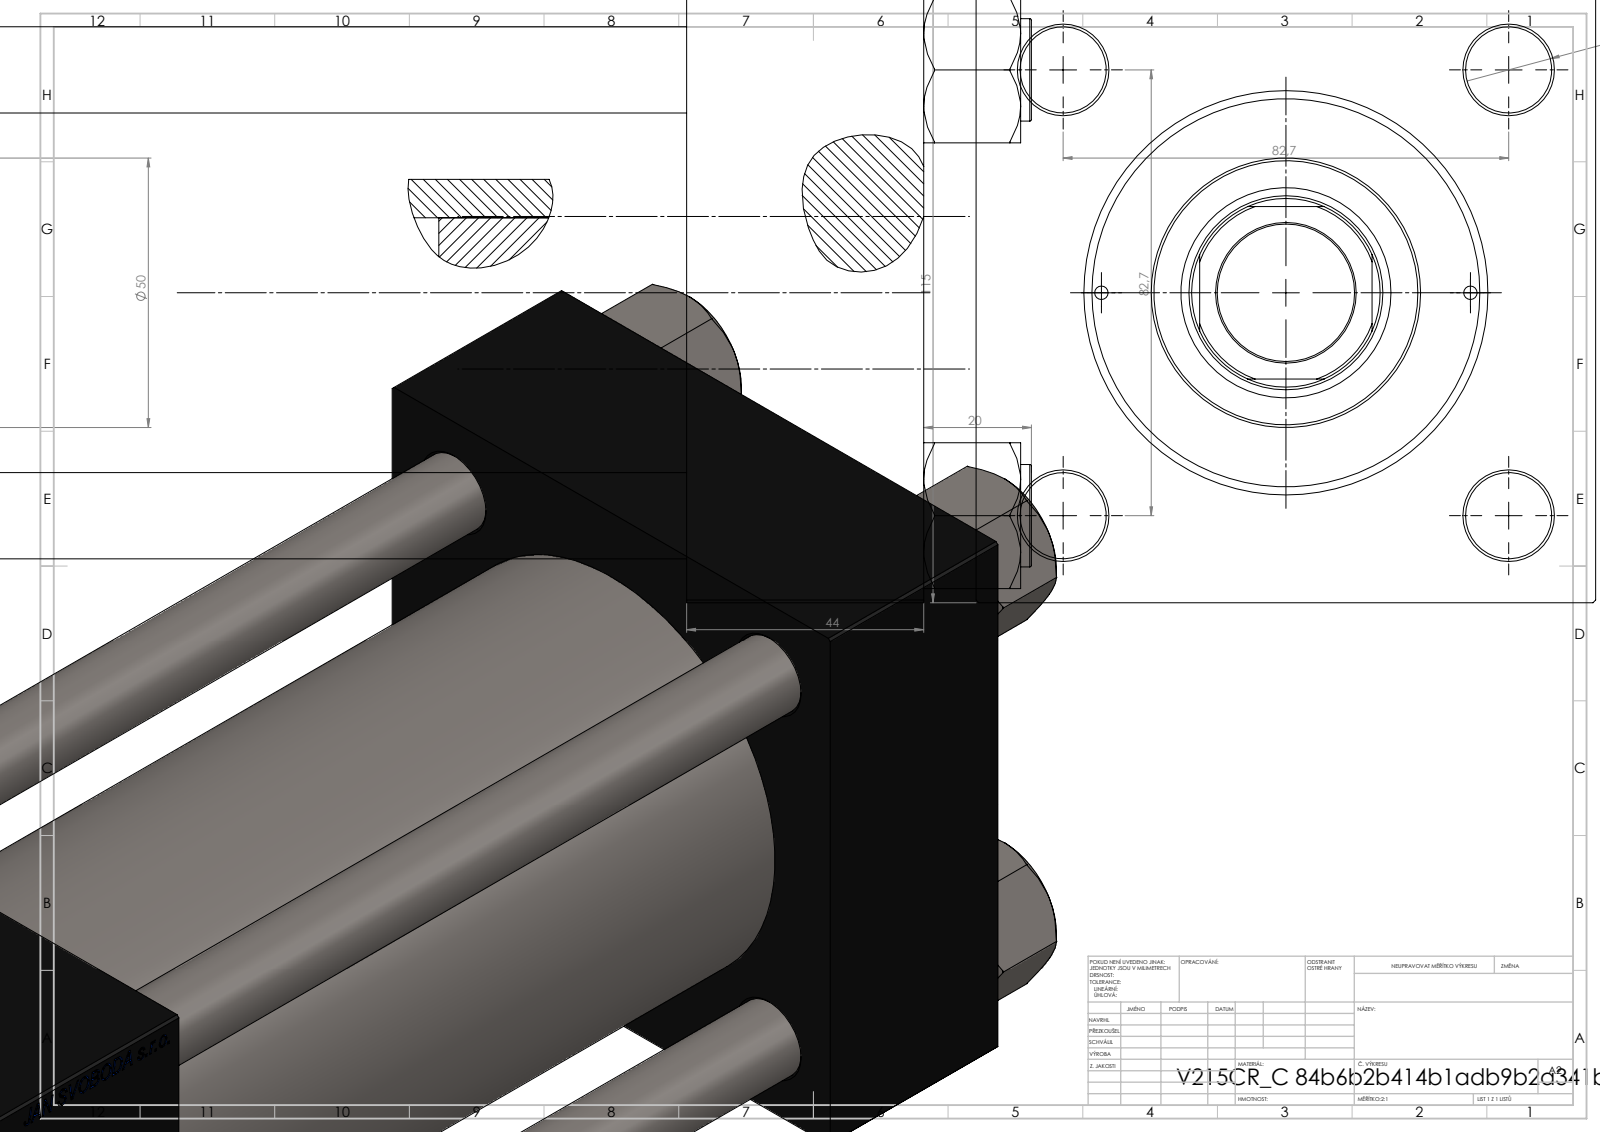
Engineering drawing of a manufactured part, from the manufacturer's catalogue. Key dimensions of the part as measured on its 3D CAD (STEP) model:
Part name (STEP PRODUCT): V215CR_VCP_C; V215CR_C_Body; NUT_M5_C; V215_VC_A (+1 more)
STEP written by: SolidWorks 2019 (CONFIG_CONTROL_DESIGN)
Units: millimetres
Bodies: 11 solids, 1202 faces (576 planar, 90 cylindrical, 536 other)
Overall size (bounding box): 335 × 115 × 115
Volume: 2 060 000 mm³ · Surface area: 356 256 mm²
Round holes (diameter × count): ⌀16 ×4, ⌀2.5 ×2, ⌀7 ×2, ⌀26.44 ×2, ⌀35 ×2, ⌀25.5 ×1, ⌀36 ×1, ⌀39 ×1, ⌀61 ×1, ⌀72 ×1, ⌀80 ×1
Round bosses / shafts (diameter × count): ⌀19 ×4, ⌀86 ×1, ⌀50 ×1
Partial cylindrical surfaces — rounded edges, fillets, slot ends (radius × count): R17.5 ×1
Main face-to-face distances: 115, 44, 284, 240, 215, 171, 69, 255.3, 211.3, 40.3
Hole centre spacings: 41.96, 58.48, 82.7, 86.17, 34.25, 116.96, 68.5, 216
